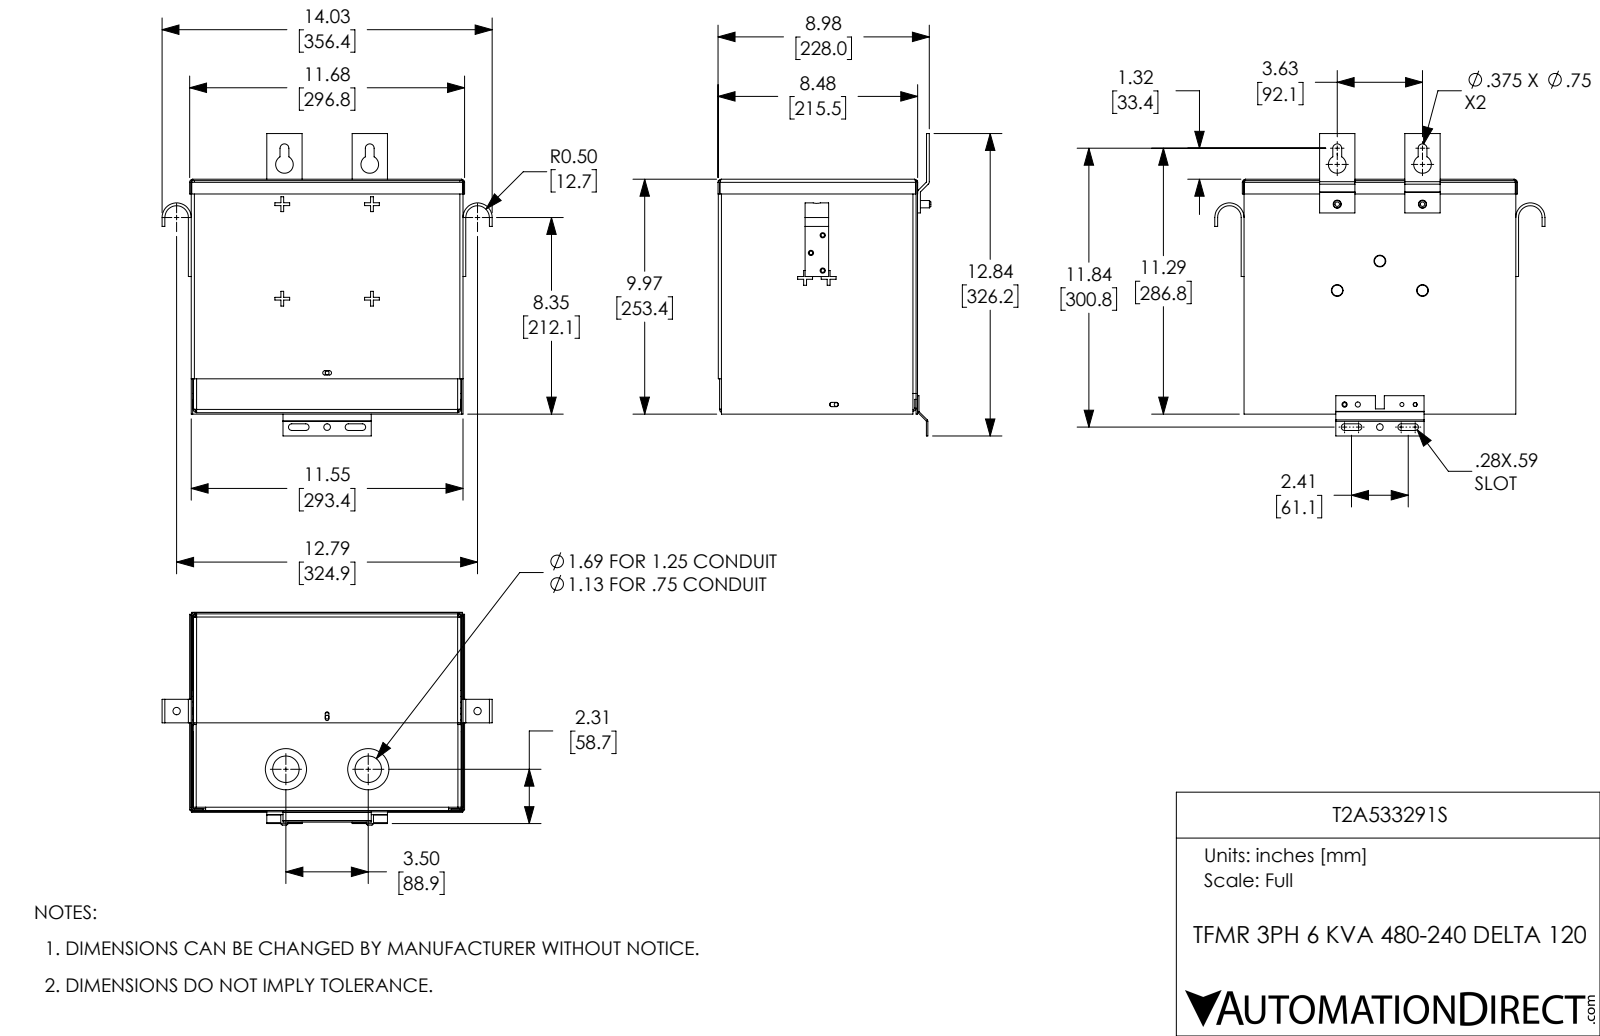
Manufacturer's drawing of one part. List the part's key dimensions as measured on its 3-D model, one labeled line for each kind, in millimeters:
Part name (STEP PRODUCT): T2A533291S
STEP written by: SolidWorks 2017 (AUTOMOTIVE_DESIGN)
Units: millimetres
Bodies: 12 solids, 602 faces (392 planar, 138 cylindrical, 72 other)
Overall size (bounding box): 356.4 × 326.2 × 229.7
Volume: 668 800 mm³ · Surface area: 869 700 mm²
Round holes (diameter × count): ⌀4.1 ×5, ⌀4.4 ×2, ⌀5.6 ×2, ⌀7.1 ×2, ⌀8 ×2, ⌀8.7 ×2, ⌀19.1 ×2, ⌀44.5 ×2, ⌀4.4 ×1, ⌀4.7 ×1, ⌀28.6 ×1, ⌀28.6 ×1
Round bosses / shafts (diameter × count): ⌀47.5 ×2, ⌀31.6 ×2, ⌀7.9 ×2
Partial cylindrical surfaces — rounded edges, fillets, slot ends (radius × count): R1.9 ×16, R3.4 ×16, R2.4 ×8, R3.6 ×4, R0.5 ×2, R0.8 ×2, R2 ×2, R2 ×2
Main face-to-face distances: 1.5, 213.6, 212.1, 250.3, 215.1, 1.5, 291.9, 1.7, 248.7, 293.4
Hole centre spacings: 14.3, 34.1, 41.6, 42.8, 45.2, 51.2, 61.9, 71.7
